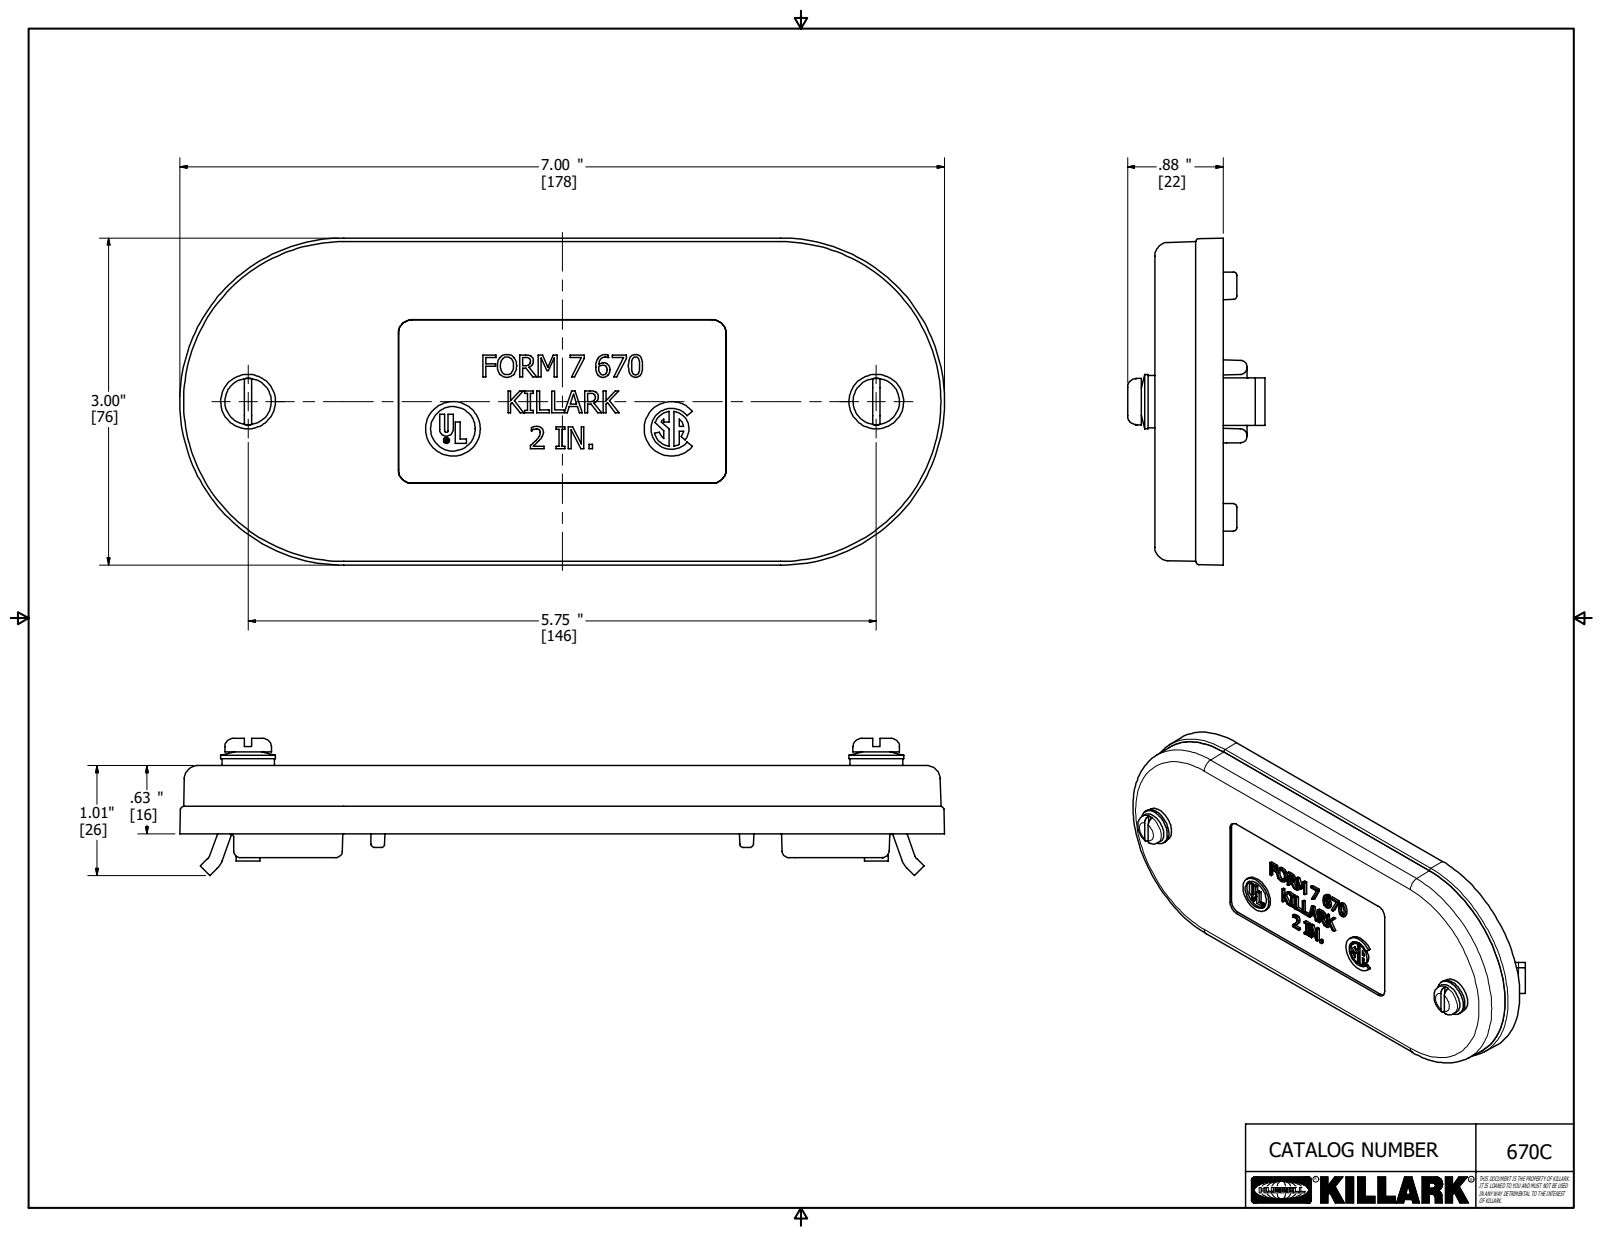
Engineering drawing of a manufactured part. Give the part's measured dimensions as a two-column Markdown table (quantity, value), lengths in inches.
| quantity | value |
| --- | --- |
| part name | 670C; 17716; 18038; 18033 |
| STEP written by | Autodesk Inventor 2018 (AUTOMOTIVE_DESIGN) |
| units | inches |
| bodies | 7 solids, 679 faces (341 planar, 144 cylindrical, 194 other) |
| overall size | 7 × 3 × 1.258 |
| volume | 6.364 in³ |
| surface area | 66.97 in² |
| round holes (diameter × count) | 0.177 × 2, 0.047 × 1, 0.407 × 1 |
| round bosses / shafts (diameter × count) | 0.5 × 3, 0.48 × 2, 0.425 × 2, 0.216 × 2, 0.056 × 1 |
| partial cylindrical surfaces (radius × count) | 0.031 × 32, 0.062 × 25, 0.06 × 13, 0.125 × 6, 0.187 × 5, 0.028 × 2, 0.006 × 1, 0.009 × 1 |
| main face-to-face distances | 0.219, 0.187, 0.031, 0.625, 0.594, 0.406, 0.222, 0.25, 0.028, 1.881 |
| hole center spacings | 0.122, 1.85, 1.892, 3.883, 3.951, 5.75 |
